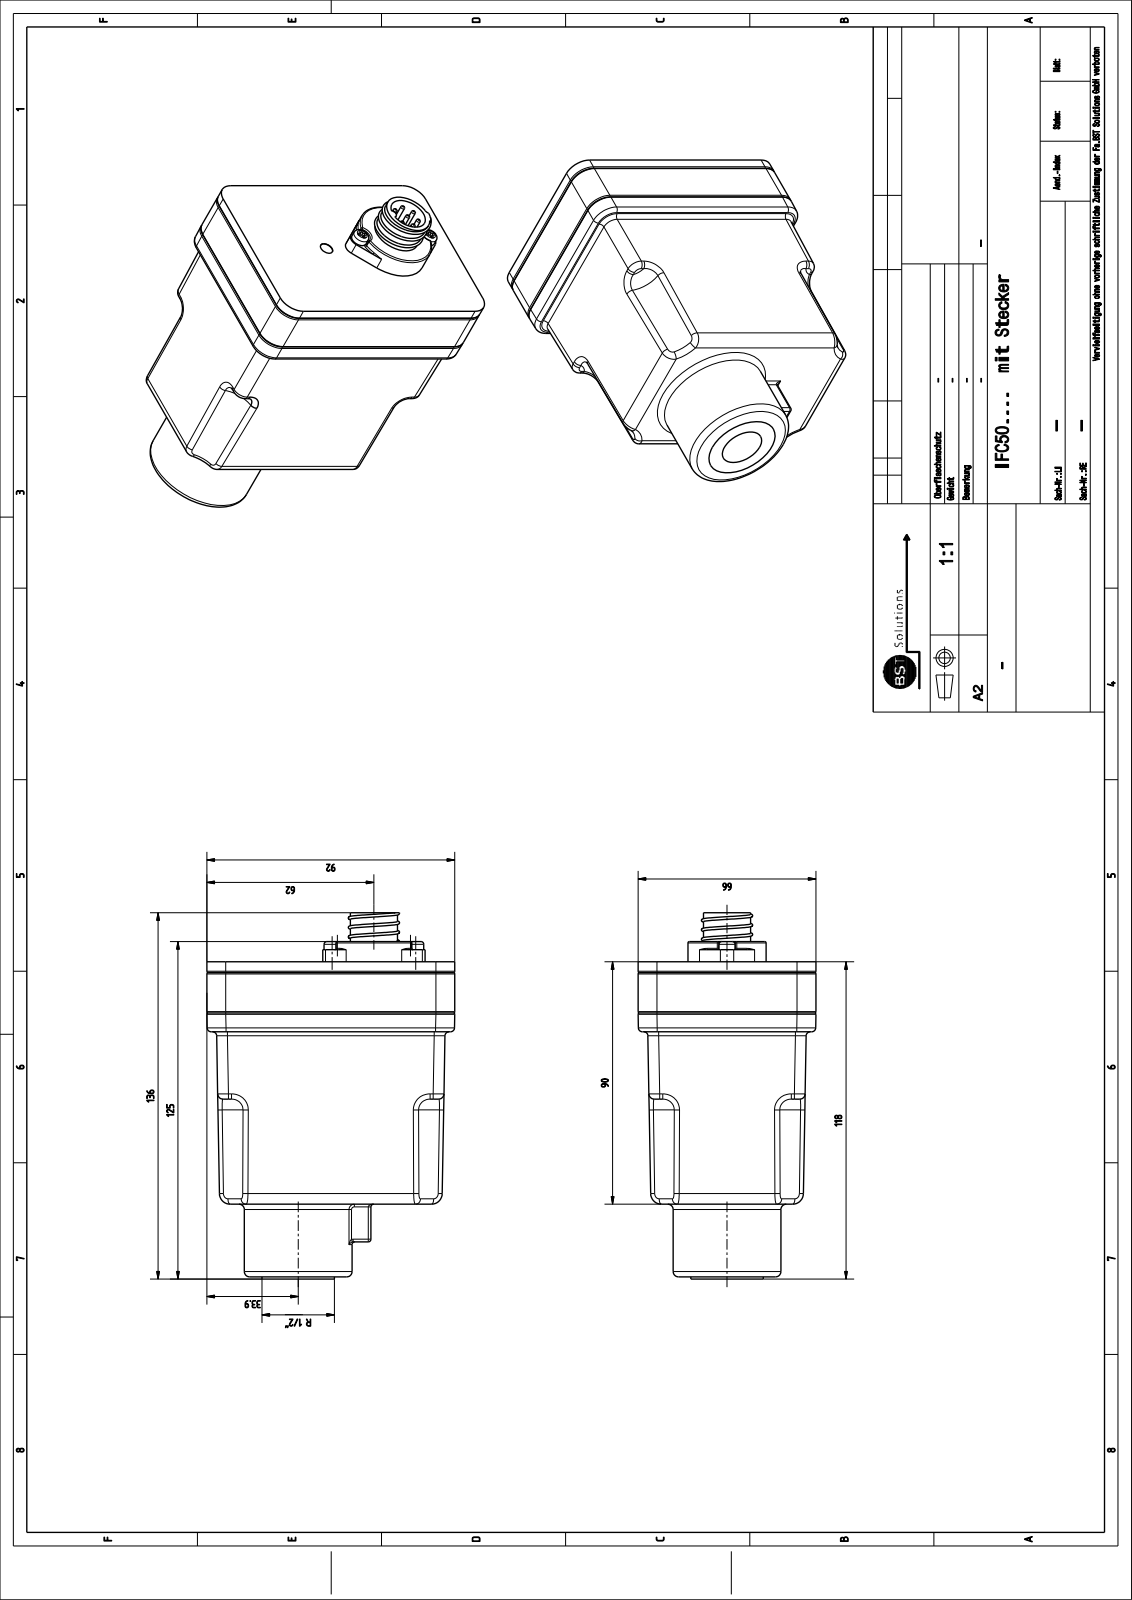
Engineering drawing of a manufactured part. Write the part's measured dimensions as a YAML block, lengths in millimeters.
part_name: "1616410443; 1615455413; 1615456404; 1615281506 (+1 more)"
step_written_by: "Spatial InterOp 3D (AUTOMOTIVE_DESIGN)"
units: millimeters
bodies: {solids: 5, faces: 306, planar: 83, cylindrical: 113, other: 110}
overall_size: [136.4, 92, 66]
volume: 499148
surface_area: 72576
round_holes:
  - {diameter: 2.5, count: 2}
  - {diameter: 3.2, count: 2}
  - {diameter: 3.3, count: 1}
  - {diameter: 5, count: 1}
  - {diameter: 14, count: 1}
  - {diameter: 16, count: 1}
  - {diameter: 22, count: 1}
  - {diameter: 23, count: 1}
  - {diameter: 24, count: 1}
round_bosses_or_shafts:
  - {diameter: 1.5, count: 7}
  - {diameter: 6, count: 2}
  - {diameter: 40, count: 1}
  - {diameter: 29, count: 1}
  - {diameter: 26.9, count: 1}
  - {diameter: 21.6, count: 1}
  - {diameter: 17.5, count: 1}
partial_cylinders:
  - {radius: 0.5, count: 30}
  - {radius: 1, count: 10}
  - {radius: 1.5, count: 9}
  - {radius: 4, count: 8}
  - {radius: 7, count: 8}
  - {radius: 2, count: 4}
  - {radius: 10, count: 4}
  - {radius: 3.5, count: 2}
face_to_face_distances: [15, 19, 4, 71, 86, 90, 66, 3.48, 92, 27]
hole_center_spacings: [15.5, 12.5, 12.6, 28, 28.1, 31, 43.5, 43.6]
